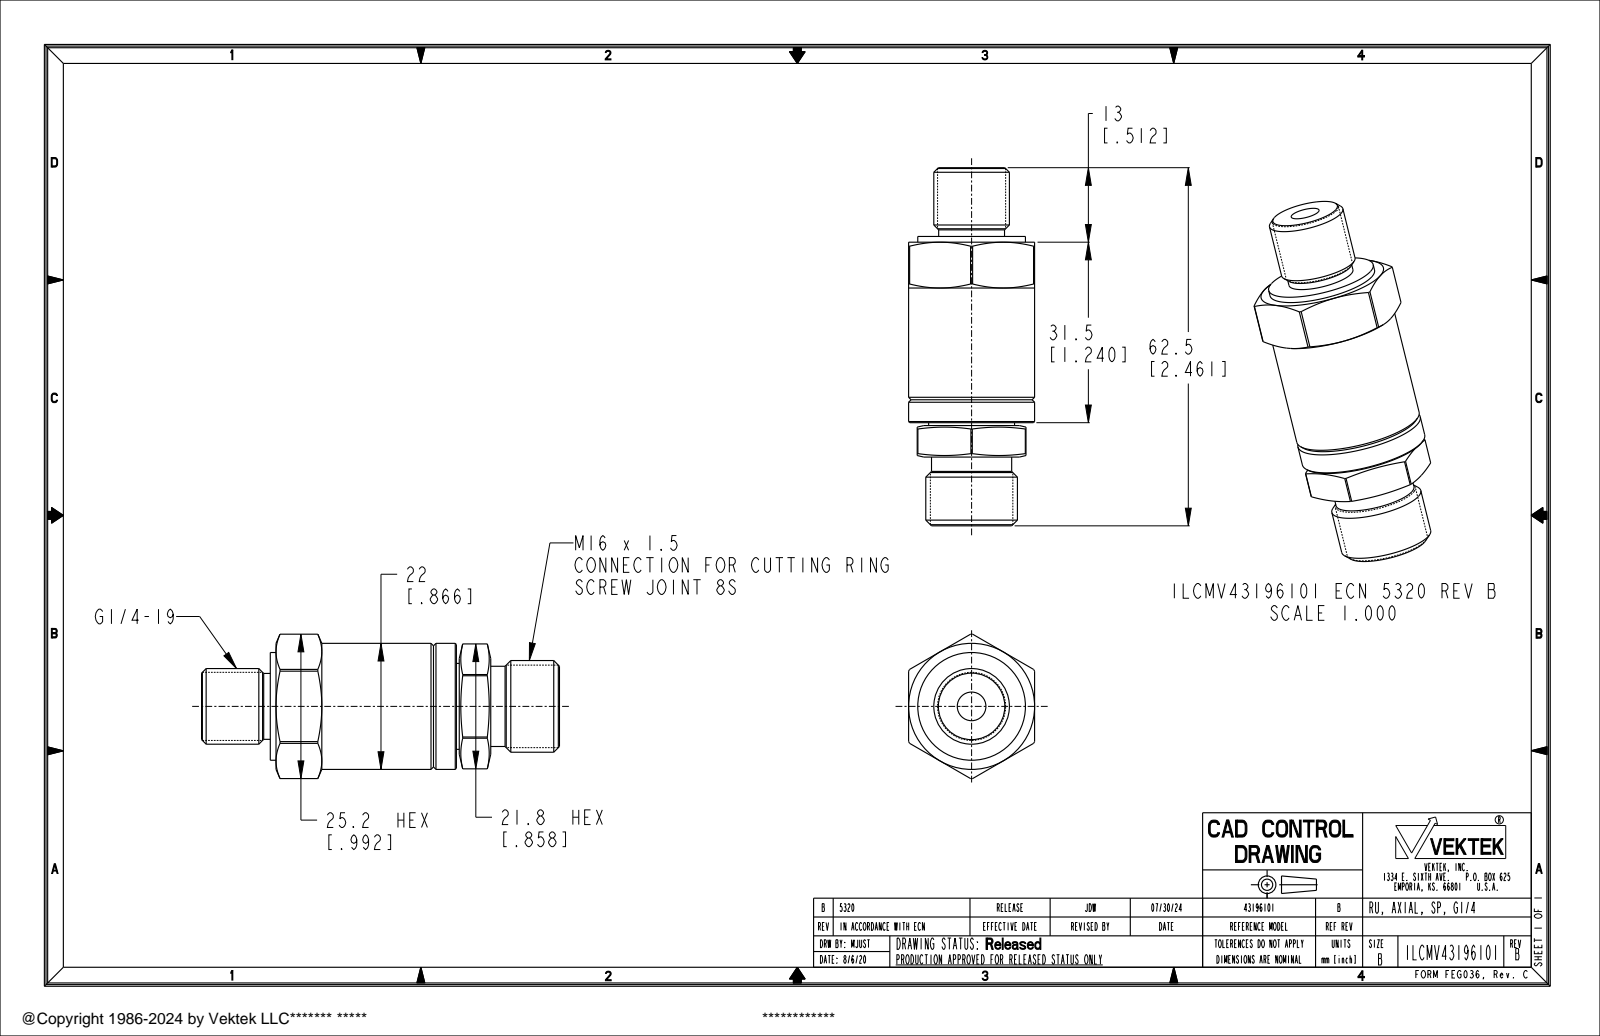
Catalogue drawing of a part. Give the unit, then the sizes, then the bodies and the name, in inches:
Units: inches
Overall size (bounding box): 2.461 × 0.992 × 0.866
Round holes (diameter × count): ⌀0.197 ×1
Round bosses / shafts (diameter × count): ⌀0.866 ×1, ⌀0.74 ×1, ⌀0.63 ×1, ⌀0.591 ×1, ⌀0.567 ×1, ⌀0.551 ×1, ⌀0.52 ×1, ⌀0.468 ×1
Partial cylindrical surfaces — rounded edges, fillets, slot ends (radius × count): R0.429 ×1, R0.496 ×1
Main face-to-face distances: 0.059, 0.807, 0.866, 1.28, 0.748, 0.472, 1.988, 1.24, 0.039, 1.752
Volume: 1.014 in³ · Surface area: 10.3 in²
Bodies: 1 solid, 86 faces (20 planar, 34 cylindrical, 32 other)
Part name (STEP PRODUCT): ILCMV43196101
STEP written by: CREO PARAMETRIC BY PTC INC, 2021164 (AUTOMOTIVE_DESIGN)
